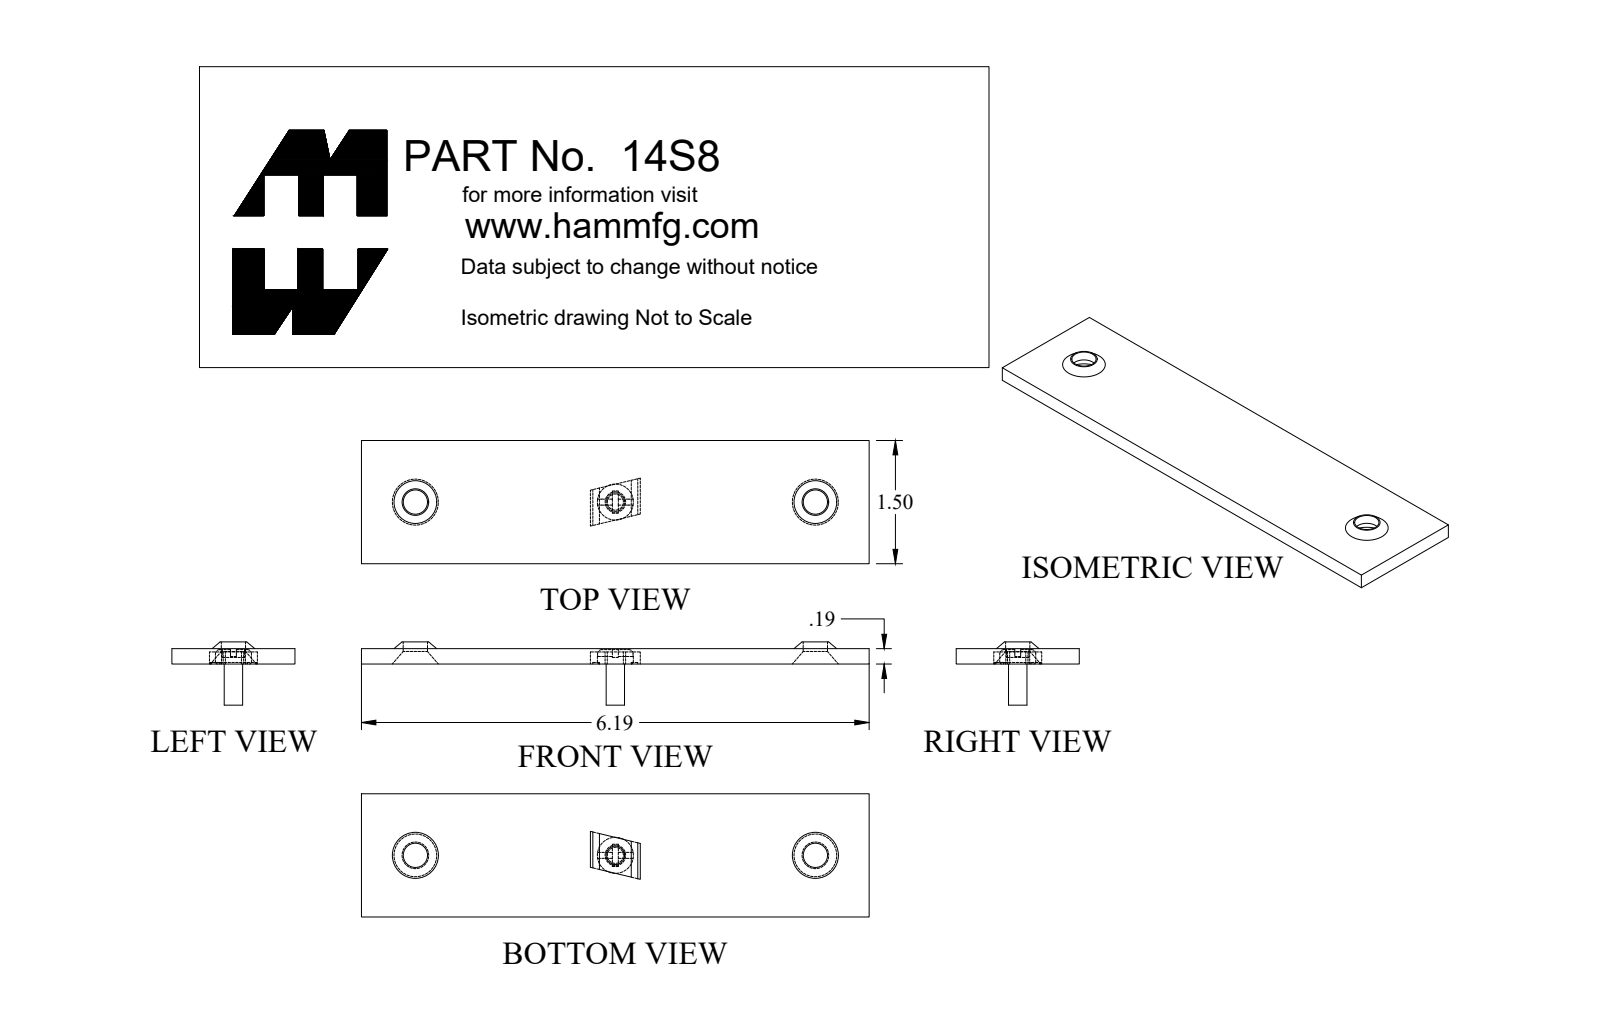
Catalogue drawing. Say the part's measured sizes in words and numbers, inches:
The part is named "14S8". Its 3-D file was written by "SolidWorks 2018 (AUTOMOTIVE_DESIGN)". It is 1 solid with 14 faces: 8 planar, 2 cylindrical and 4 other. Overall it measures 6.187 by 1.5 by 0.27 inches. Its volume is 1.706 cubic inches and its surface area 21.66 square inches. Round holes: 2 of diameter 0.296. The main face-to-face distances are 0.188, 1.5, 6.187, 0.27, 0.082. The hole center spacings are 4.875.
